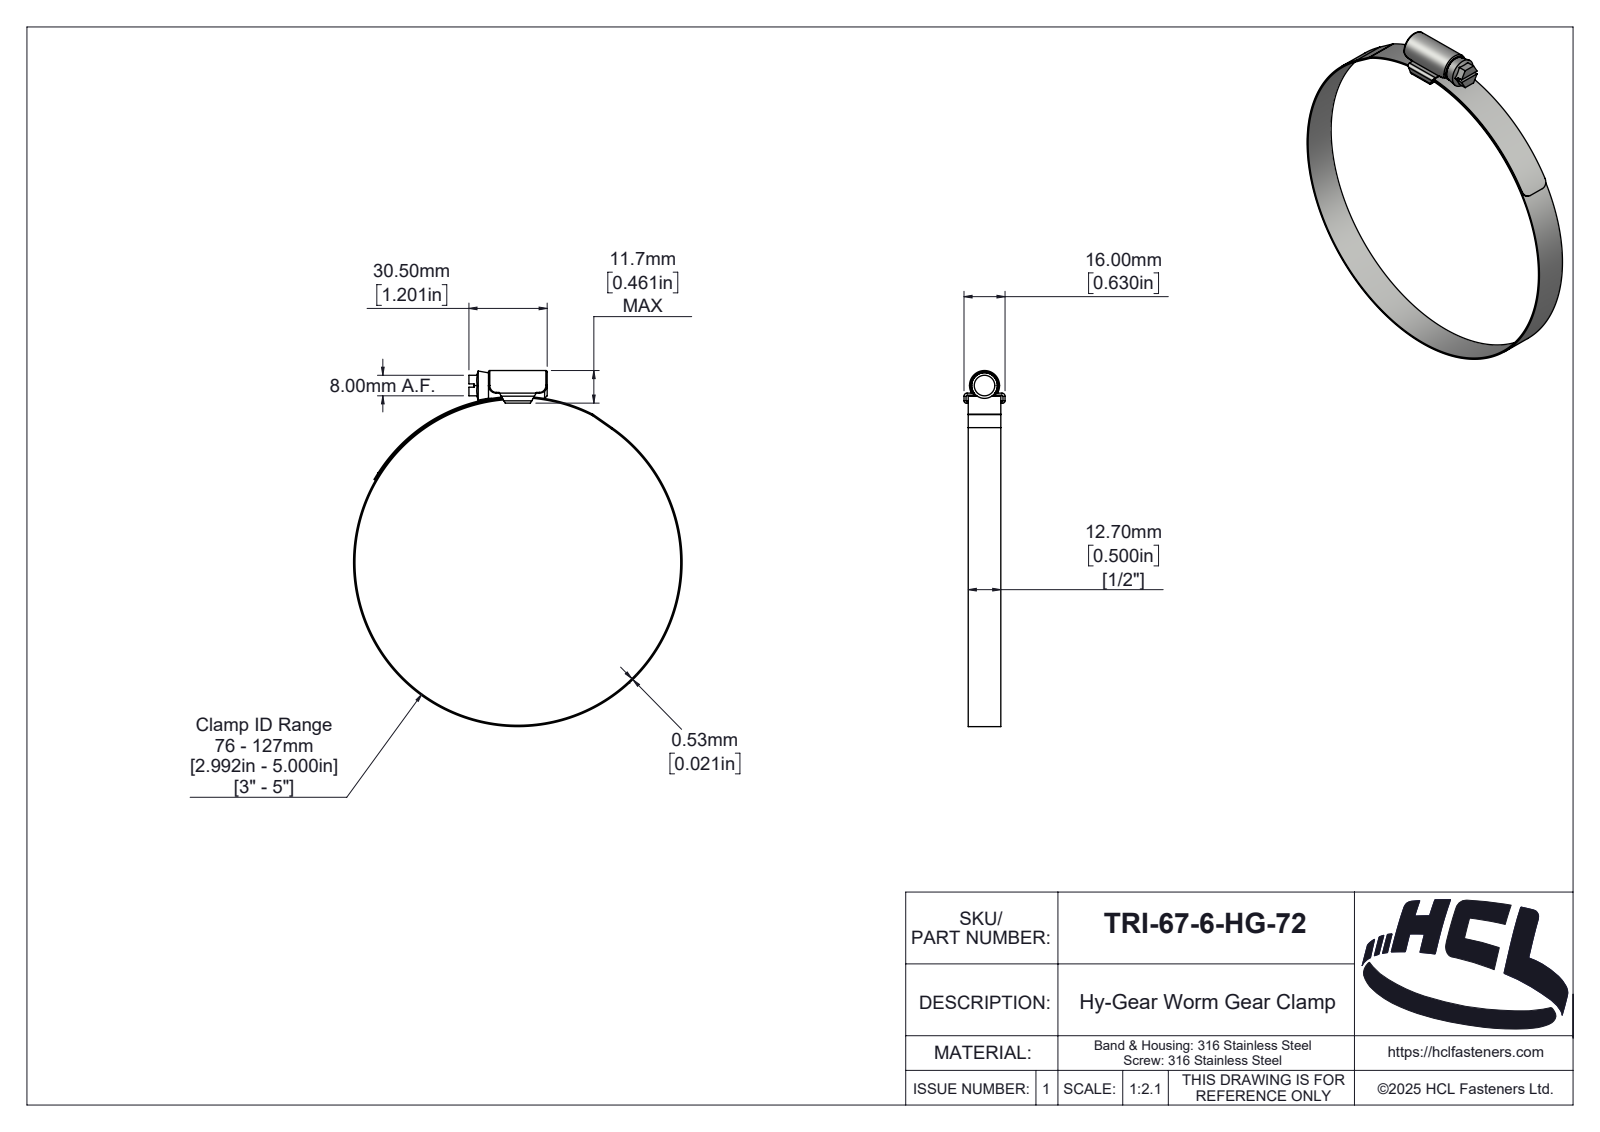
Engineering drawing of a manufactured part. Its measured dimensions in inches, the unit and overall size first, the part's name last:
Units: inches
Overall size (bounding box): 5.462 × 5.042 × 0.63
Round holes (diameter × count): ⌀5 ×1
Round bosses / shafts (diameter × count): ⌀5.042 ×1, ⌀0.394 ×1
Partial cylindrical surfaces — rounded edges, fillets, slot ends (radius × count): R0.02 ×6, R0.118 ×4, R0.004 ×2, R0.035 ×2, R0.047 ×2, R0.018 ×1, R0.074 ×1, R0.079 ×1
Main face-to-face distances: 0.5, 0.031, 0.122, 0.021, 0.091, 0.154, 1.201, 0.065, 0.565, 0.598
Volume: 0.375 in³ · Surface area: 23.71 in²
Bodies: 3 solids, 189 faces (39 planar, 89 cylindrical, 61 other)
Part name (STEP PRODUCT): TRI-57-0-HG-72
STEP written by: SolidWorks 2025 (AUTOMOTIVE_DESIGN)
